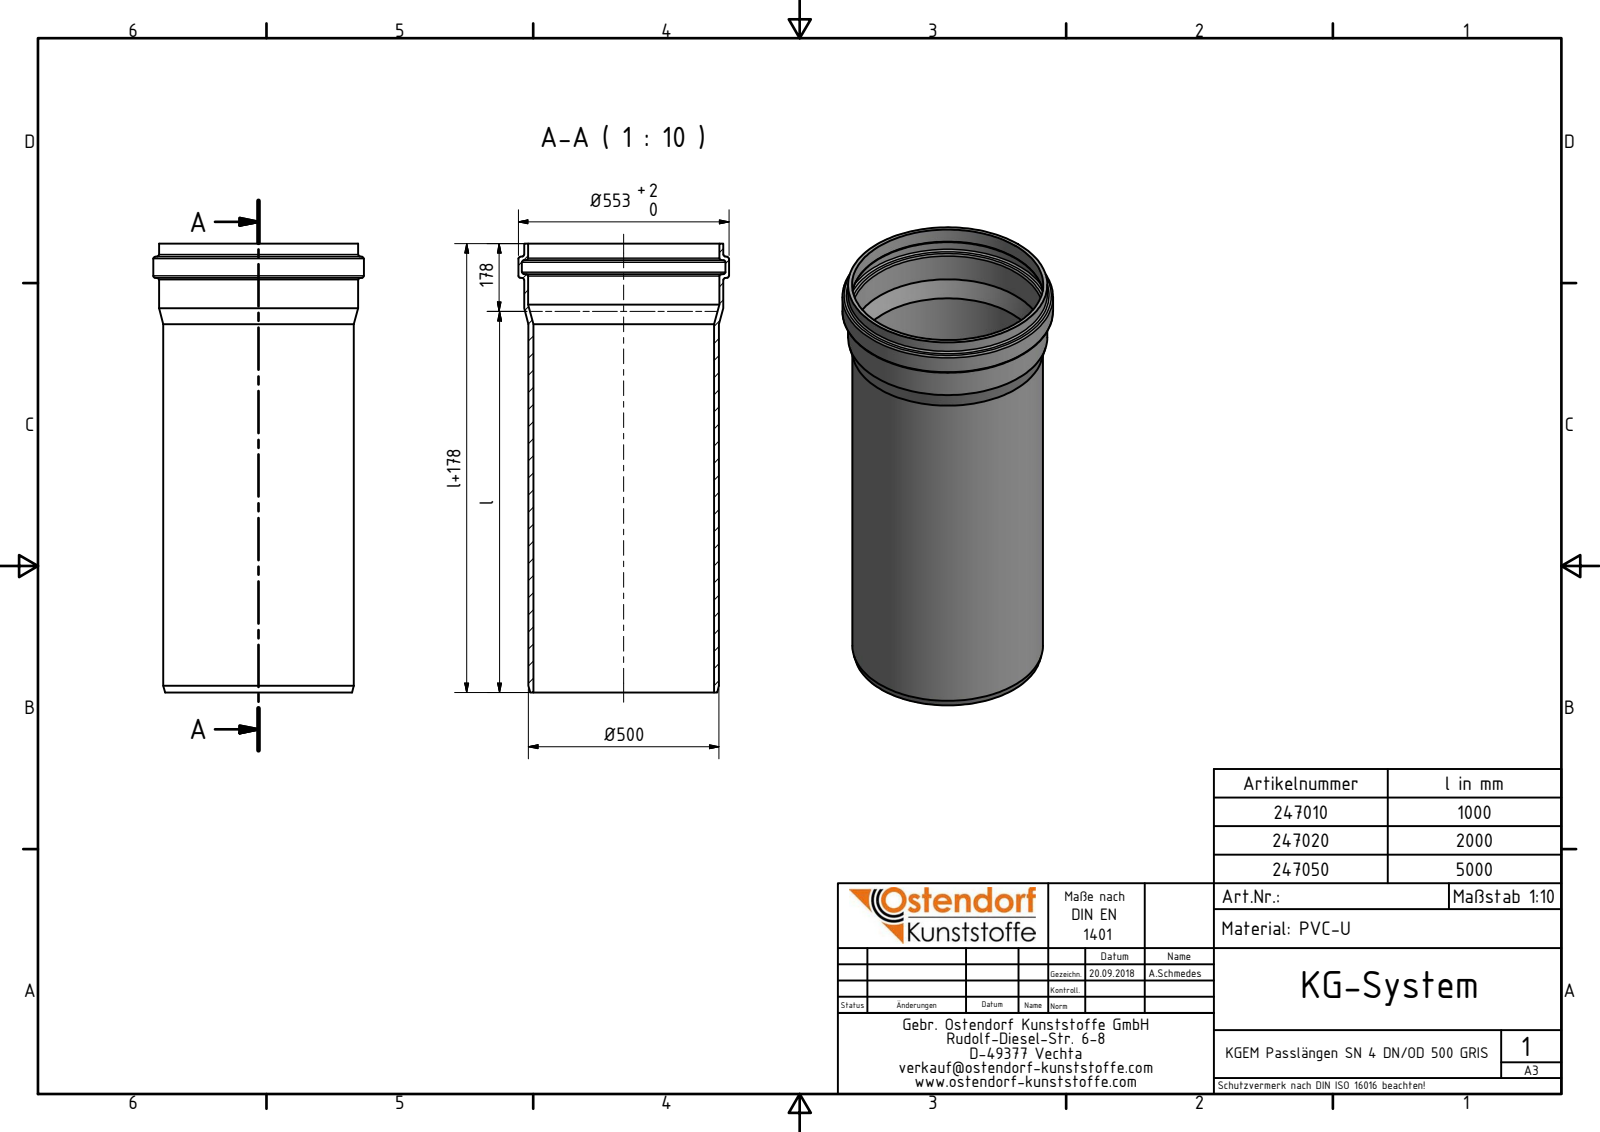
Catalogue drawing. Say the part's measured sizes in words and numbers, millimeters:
The part is named "247010 KGEM Passlängen SN 4 DN_OD 500x1000 GRIS". Its 3-D file was written by "Autodesk Inventor 2016 (AUTOMOTIVE_DESIGN)". It is 1 solid with 25 faces: 2 planar, 8 cylindrical and 15 other. Overall it measures 1178 by 553 by 553 millimeters. Its volume is 23 350 000 cubic millimeters and its surface area 3 753 000 square millimeters. Round holes: 1 of diameter 474.5, 1 of diameter 502, 1 of diameter 534.6. Round bosses or shafts: 1 of diameter 553, 1 of diameter 523, 1 of diameter 500.5. The main face-to-face distances are 1178.
